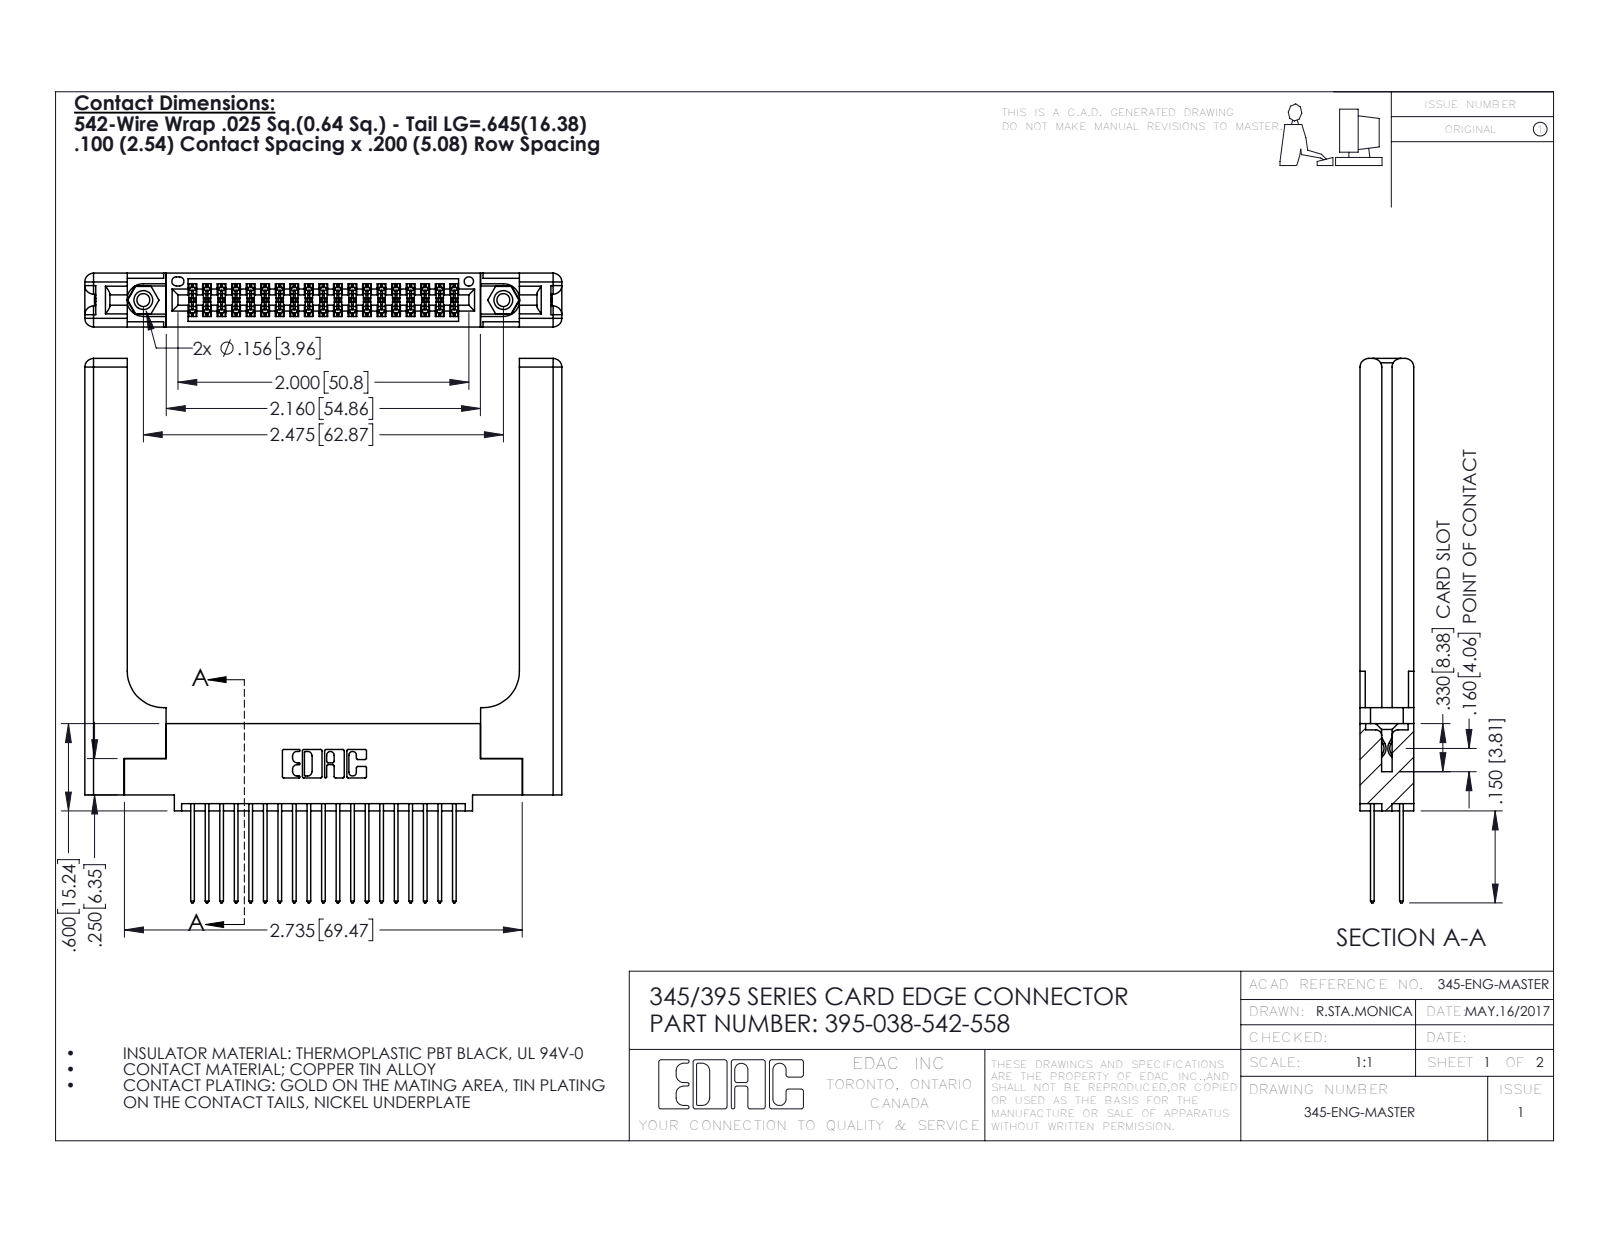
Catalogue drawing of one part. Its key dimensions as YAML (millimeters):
part_name: "345-250-001_345-250-001-102; 345-220-058_345-220-058; 395-038-542-558; 345 Part_0.110 Offset - 0.156 Dia-TH (+1 more)"
step_written_by: "SolidWorks 2016 (CONFIG_CONTROL_DESIGN)"
units: millimeters
bodies: {solids: 43, faces: 2286, planar: 1486, cylindrical: 740, other: 60}
overall_size: [95, 83.3, 9.4]
volume: 16450
surface_area: 17330
round_holes:
  - {diameter: 2.3, count: 2}
  - {diameter: 3.2, count: 2}
  - {diameter: 4, count: 2}
  - {diameter: 1.6, count: 1}
round_bosses_or_shafts:
  - {diameter: 3.9, count: 2}
partial_cylinders:
  - {radius: 0.2, count: 57}
  - {radius: 0.3, count: 38}
  - {radius: 0.3, count: 22}
  - {radius: 1.5, count: 16}
  - {radius: 0.2, count: 6}
  - {radius: 0.8, count: 6}
  - {radius: 0.7, count: 3}
  - {radius: 0.4, count: 2}
face_to_face_distances: [9.4, 1.8, 7.6, 5.1, 2.5, 6.9, 0.6, 5.7, 3.8, 3.8]
hole_center_spacings: [6.9, 56.9, 62.9]
